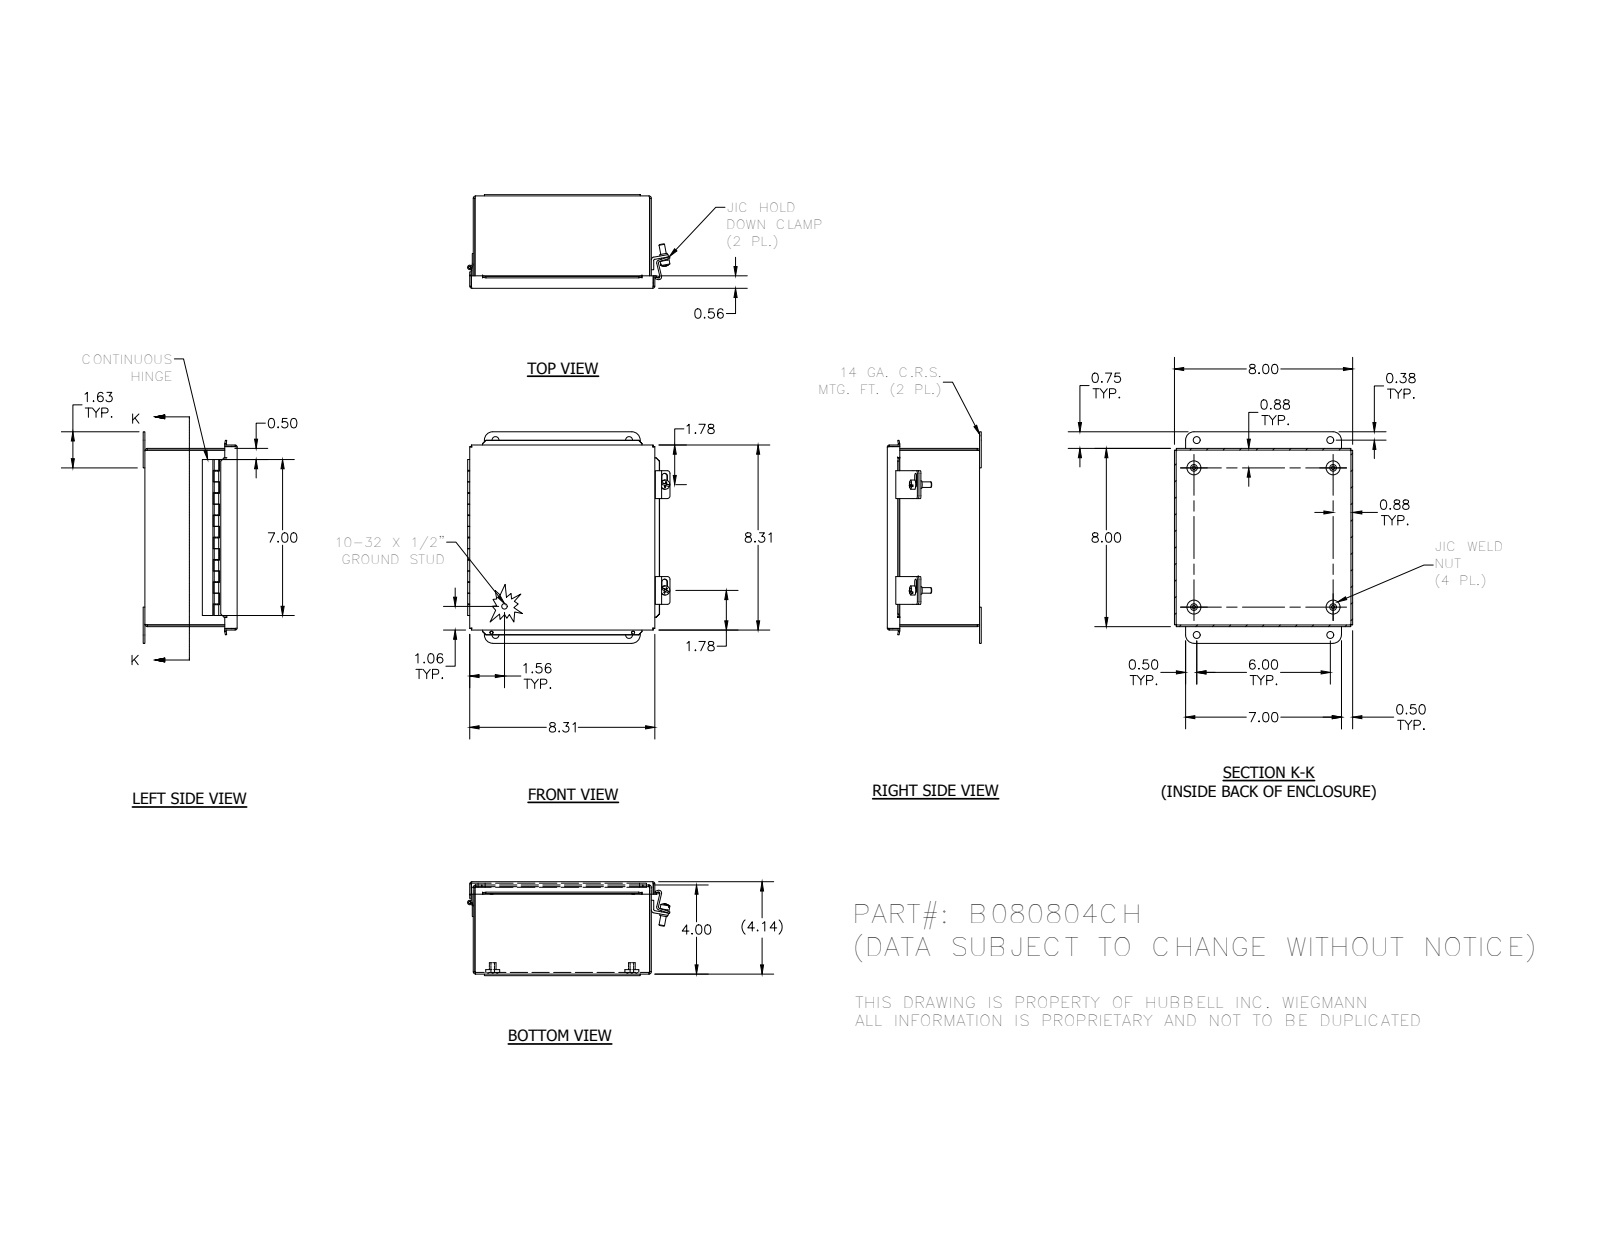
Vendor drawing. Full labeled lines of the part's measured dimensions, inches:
Part name (STEP PRODUCT): B080804CH; 3499; 3483; C1001 (+8 more)
STEP written by: Autodesk Inventor 2012 (AUTOMOTIVE_DESIGN)
Units: inches
Bodies: 20 solids, 459 faces (299 planar, 115 cylindrical, 45 other)
Overall size (bounding box): 9.5 × 9.087 × 4.219
Volume: 26.68 in³ · Surface area: 724.8 in²
Round holes (diameter × count): ⌀0.156 ×4, ⌀0.31 ×4, ⌀0.14 ×2, ⌀0.196 ×2, ⌀0.116 ×1
Round bosses / shafts (diameter × count): ⌀0.625 ×4, ⌀0.3 ×4, ⌀0.25 ×3, ⌀0.41 ×2, ⌀0.344 ×2, ⌀0.2 ×1, ⌀0.19 ×1, ⌀0.1 ×1
Partial cylindrical surfaces — rounded edges, fillets, slot ends (radius × count): R0.031 ×15, R0.105 ×8, R0.125 ×8, R0.093 ×7, R0.133 ×4, R0.375 ×4, R0.063 ×3, R0.126 ×3
Main face-to-face distances: 0.074, 7.926, 4.083, 4.144, 0.062, 4.009, 4.07, 8, 7.852, 0.075
Hole centre spacings: 1.256, 7.502, 6, 6.25, 6.25, 6.252, 8.839, 9.684
